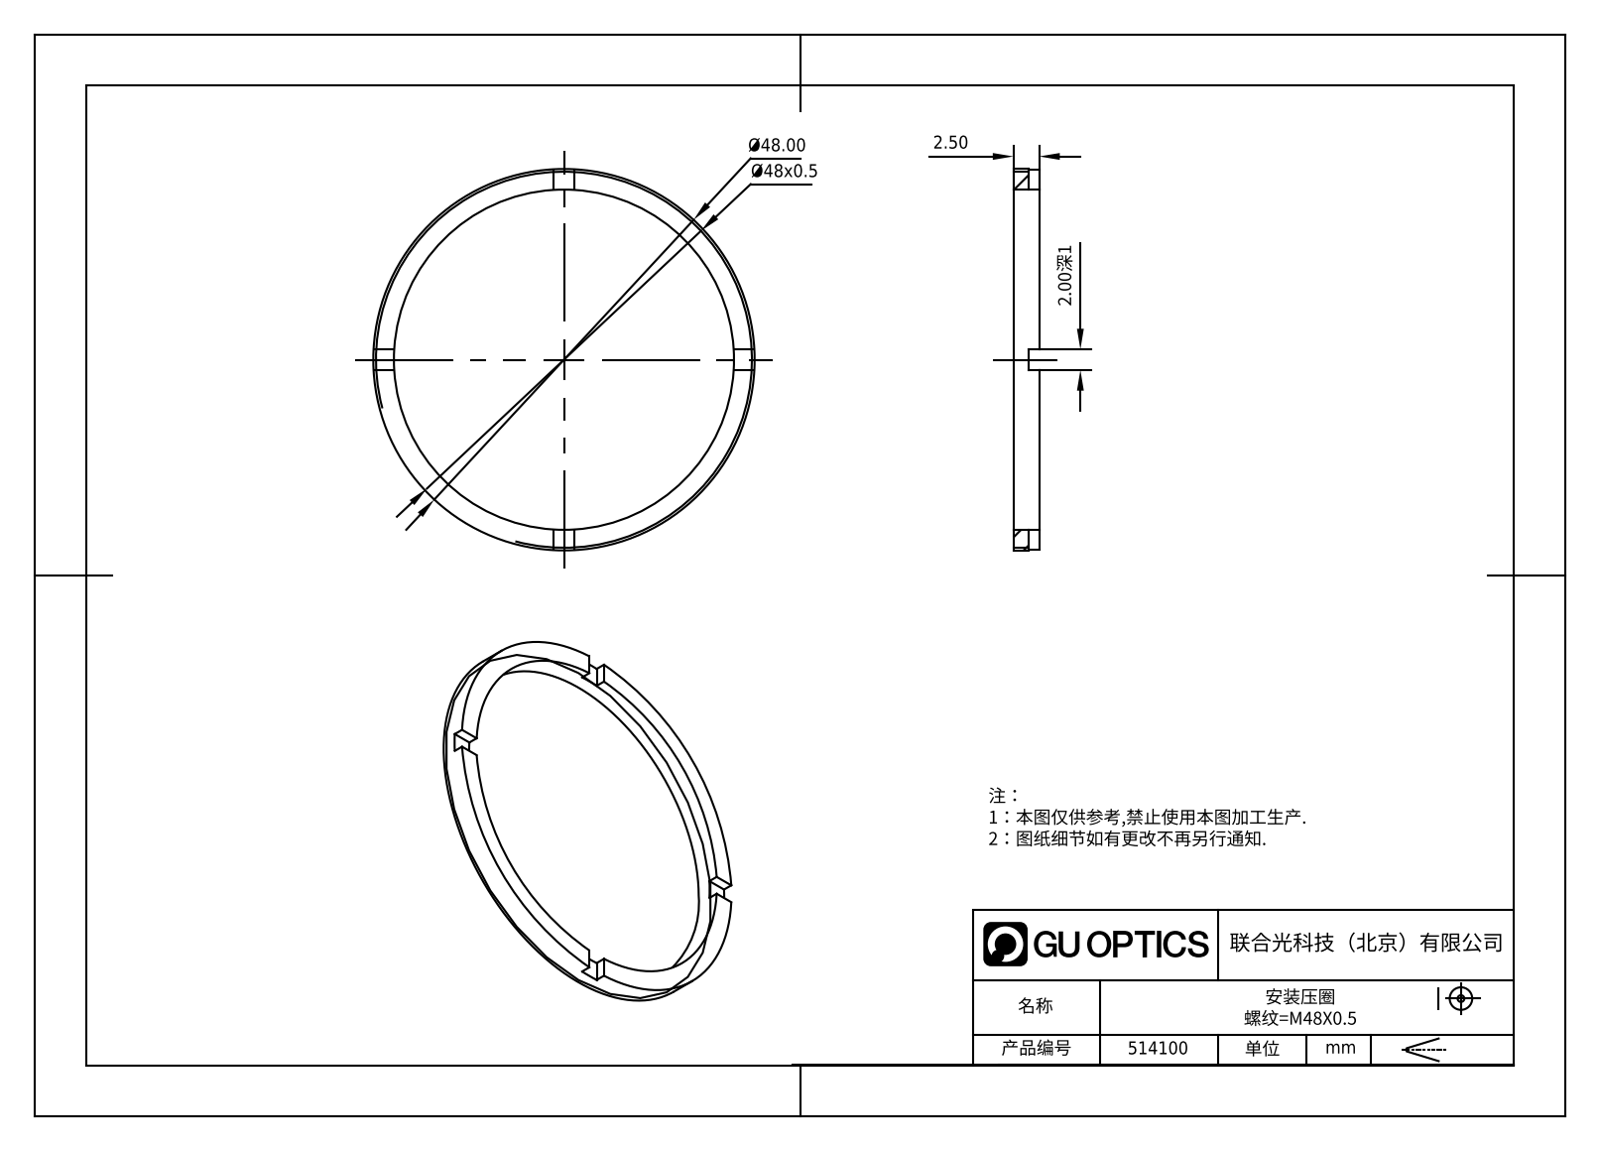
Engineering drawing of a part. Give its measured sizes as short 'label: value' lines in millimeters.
name: 514100
written by: SolidWorks 2020 (CONFIG_CONTROL_DESIGN)
unit: mm
bodies: 1 solid, 21 faces (17 planar, 4 cylindrical, 0 other)
size: 48 × 48 × 2.5
volume: 707 mm³; area: 1 301 mm²
holes: 1× ⌀44
bosses: 1× ⌀48
face distances: 2.5, 1.5, 1, 2
